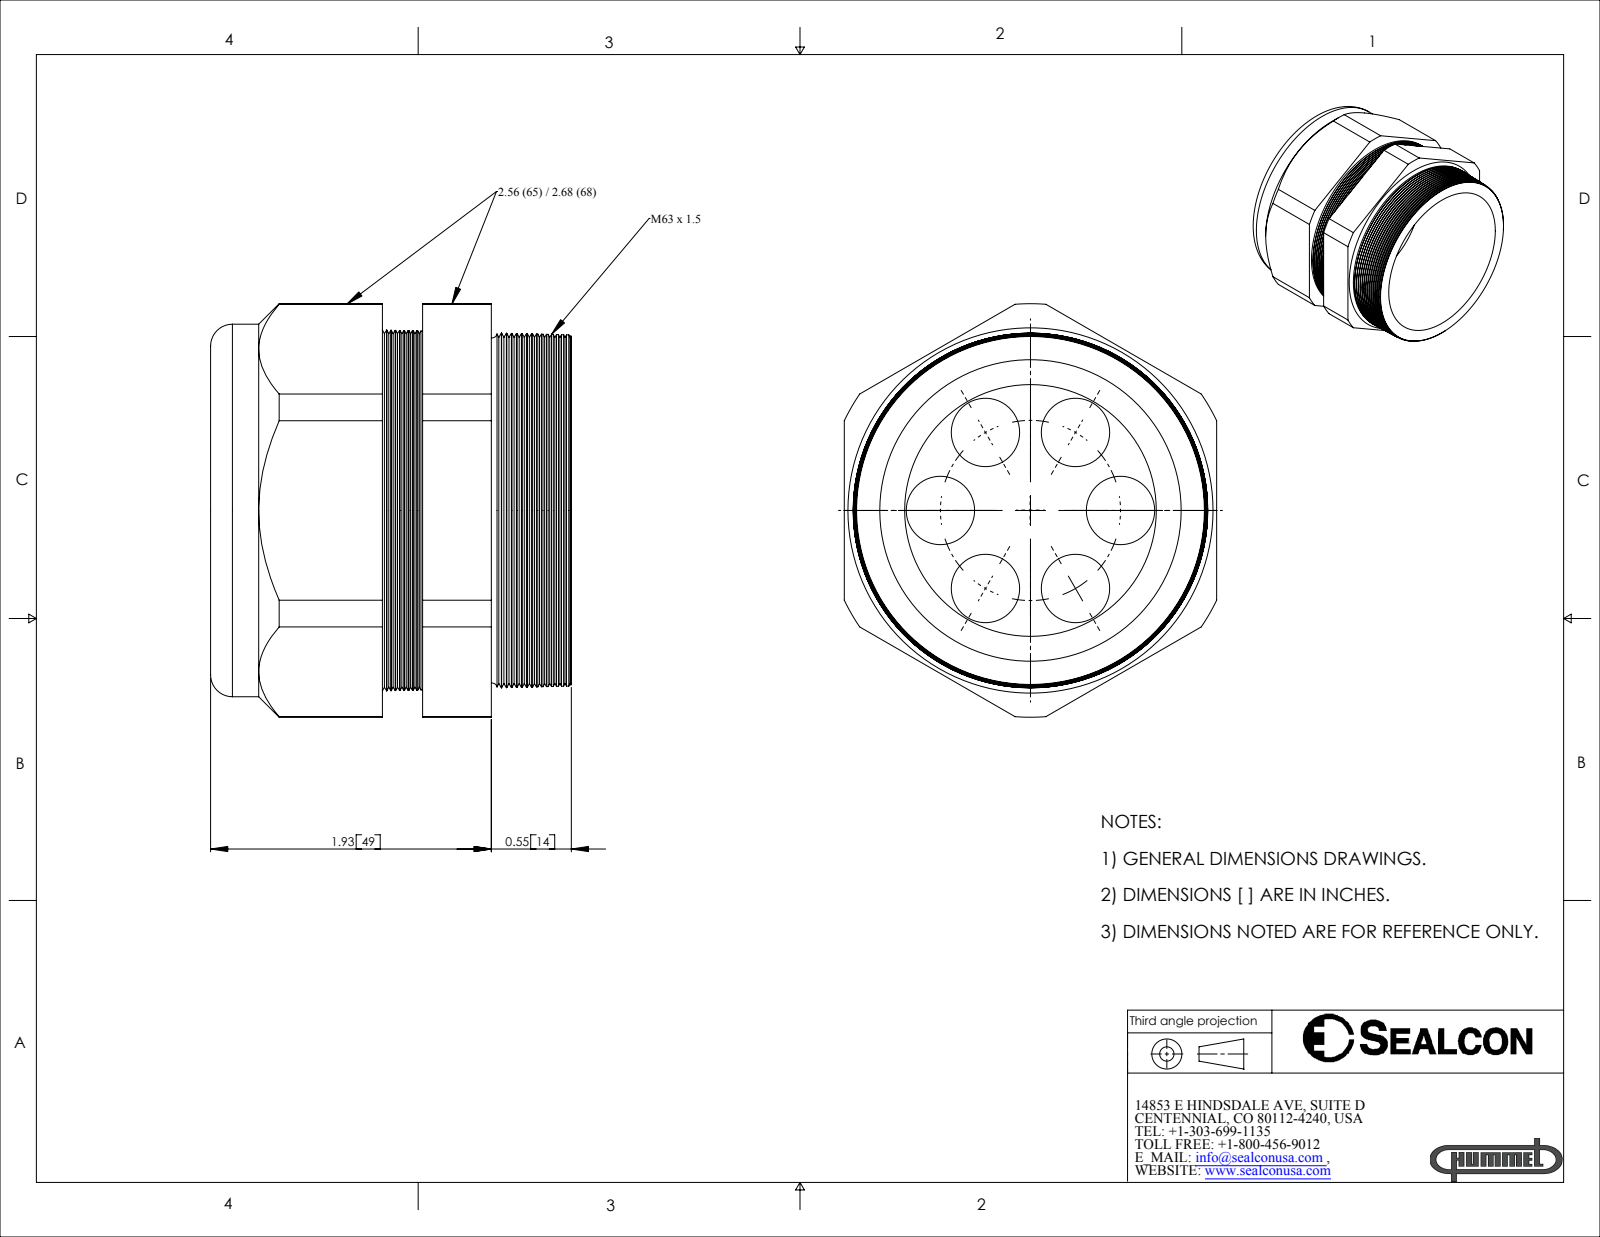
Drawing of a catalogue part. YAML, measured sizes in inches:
part_name: "CD63M2-BK"
step_written_by: "SolidWorks 2007 (CONFIG_CONTROL_DESIGN)"
units: inches
bodies: {solids: 2, faces: 210, planar: 20, cylindrical: 32, other: 158}
overall_size: [2.842, 2.56, 2.48]
volume: 7.053
surface_area: 55.81
round_holes:
  - {diameter: 0.47, count: 6}
  - {diameter: 1.71, count: 1}
  - {diameter: 1.73, count: 1}
round_bosses_or_shafts:
  - {diameter: 2.56, count: 1}
partial_cylinders:
  - {radius: 1.421, count: 1}
face_to_face_distances: [2.56, 0.5, 0.02, 0.48, 2.48, 2.46, 1.98, 1.458, 1.438, 0.958]
hole_center_spacings: [0.619, 0.619, 1.072, 1.072, 1.238, 1.238]
